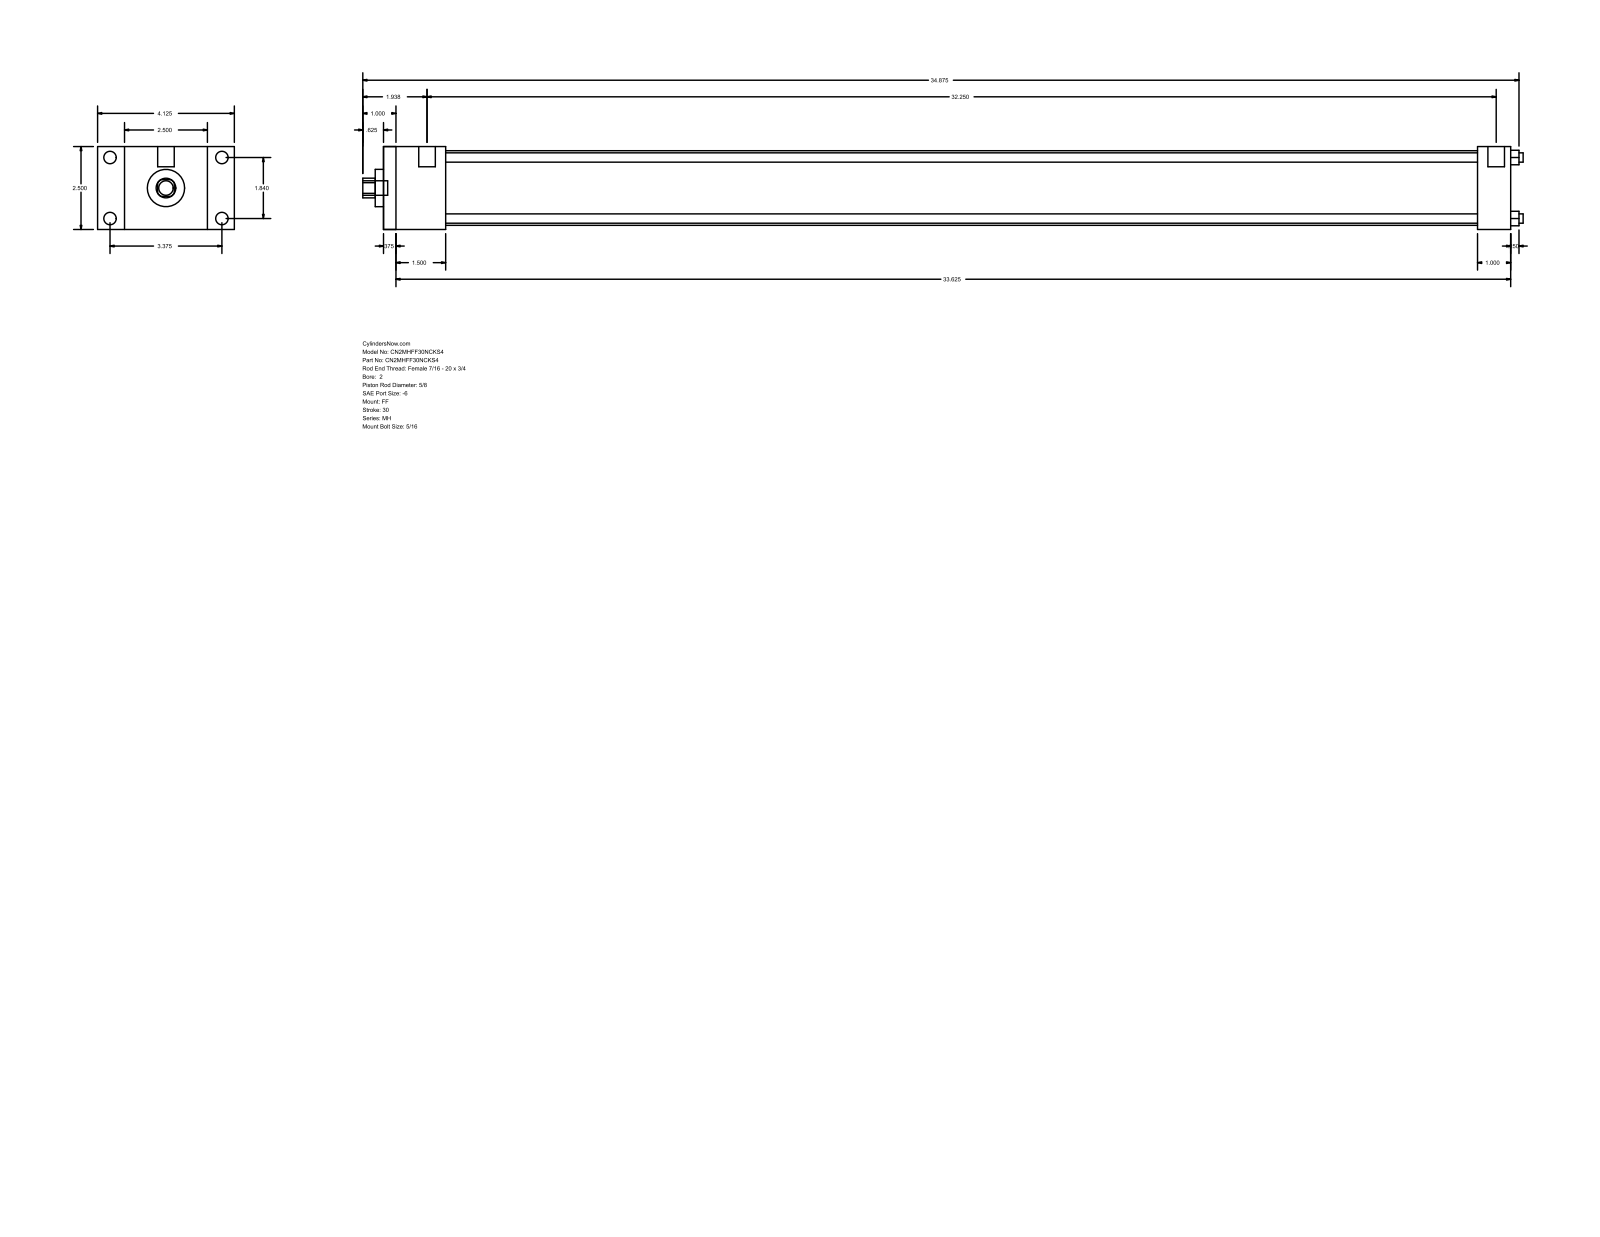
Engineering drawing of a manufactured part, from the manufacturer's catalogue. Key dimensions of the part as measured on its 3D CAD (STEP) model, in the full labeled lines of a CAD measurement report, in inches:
Part name (STEP PRODUCT): MH_FF__0200_0.625
STEP written by: GSSL Pune (CONFIG_CONTROL_DESIGN)
Units: inches
Bodies: 0 solids, 92 faces (64 planar, 28 cylindrical, 0 other)
Overall size (bounding box): 35 × 4.125 × 2.5
Round holes (diameter × count): ⌀0.281 ×4, ⌀0.625 ×1, ⌀1.125 ×1, ⌀2.25 ×1
Round bosses / shafts (diameter × count): ⌀0.375 ×4, ⌀0.219 ×4, ⌀0.5 ×2, ⌀0.437 ×1
Partial cylindrical surfaces — rounded edges, fillets, slot ends (radius × count): R0.297 ×1
Main face-to-face distances: 2.5, 34, 0.375, 33.625, 1, 1.5, 1.875, 33, 32.625, 31.125
Hole centre spacings: 1.301, 1.84, 2.602
